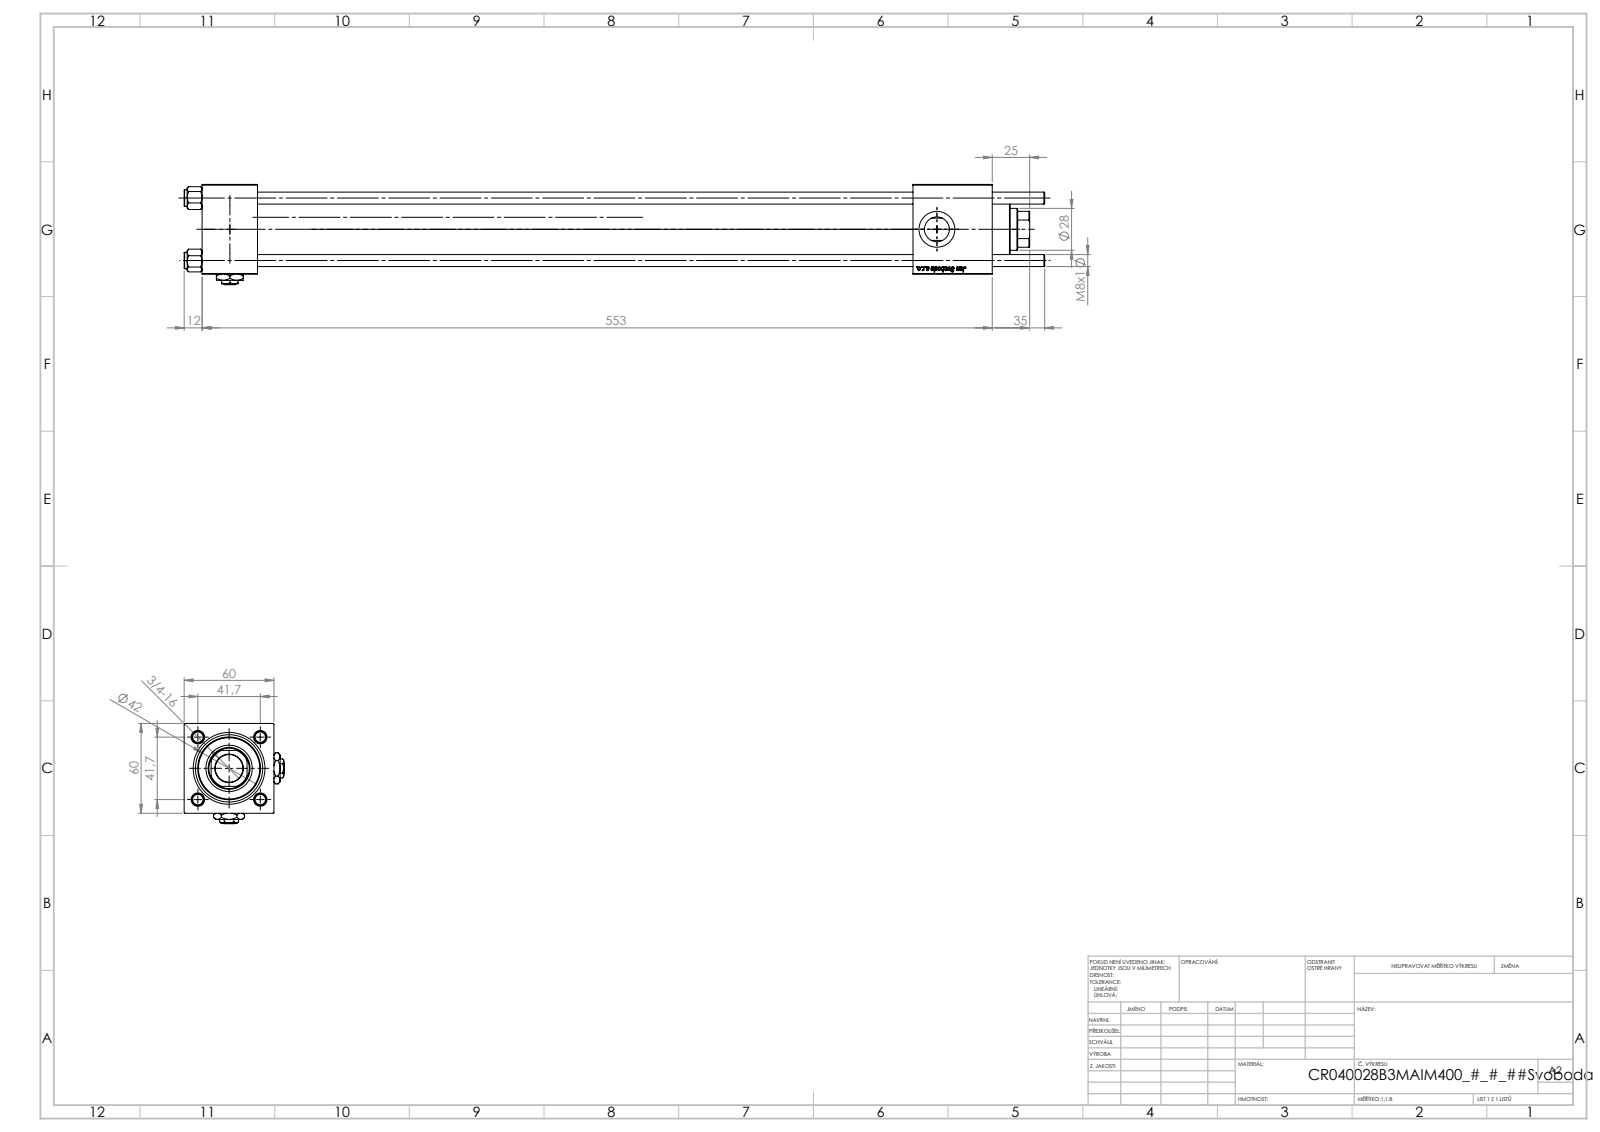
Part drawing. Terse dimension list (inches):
name: V215CR_B_TYCINKA; V215CR_VCP_B; Zatka_pro_OIL_PORT; NUT_M5_B (+2 more)
written by: SolidWorks 2019 (CONFIG_CONTROL_DESIGN)
unit: in
bodies: 13 solids, 1260 faces (480 planar, 90 cylindrical, 690 other)
size: 22.638 × 2.638 × 2.638
volume: 54.68 in³; area: 460.8 in²
holes: 4× ⌀0.315, 2× ⌀0.276, 2× ⌀0.656, 2× ⌀0.945, 1× ⌀0.63, 1× ⌀0.728, 1× ⌀1.102, 1× ⌀1.22, 1× ⌀1.575, 1× ⌀1.772
bosses: 4× ⌀0.433, 1× ⌀1.811, 1× ⌀1.654
rounds: 1× R0.531
face distances: 2.362, 1.457, 18.701, 17.244, 2.087, 19.657, 18.201, 0.957, 20.787, 19.331
hole spacings: 1.161, 1.642, 2.322
